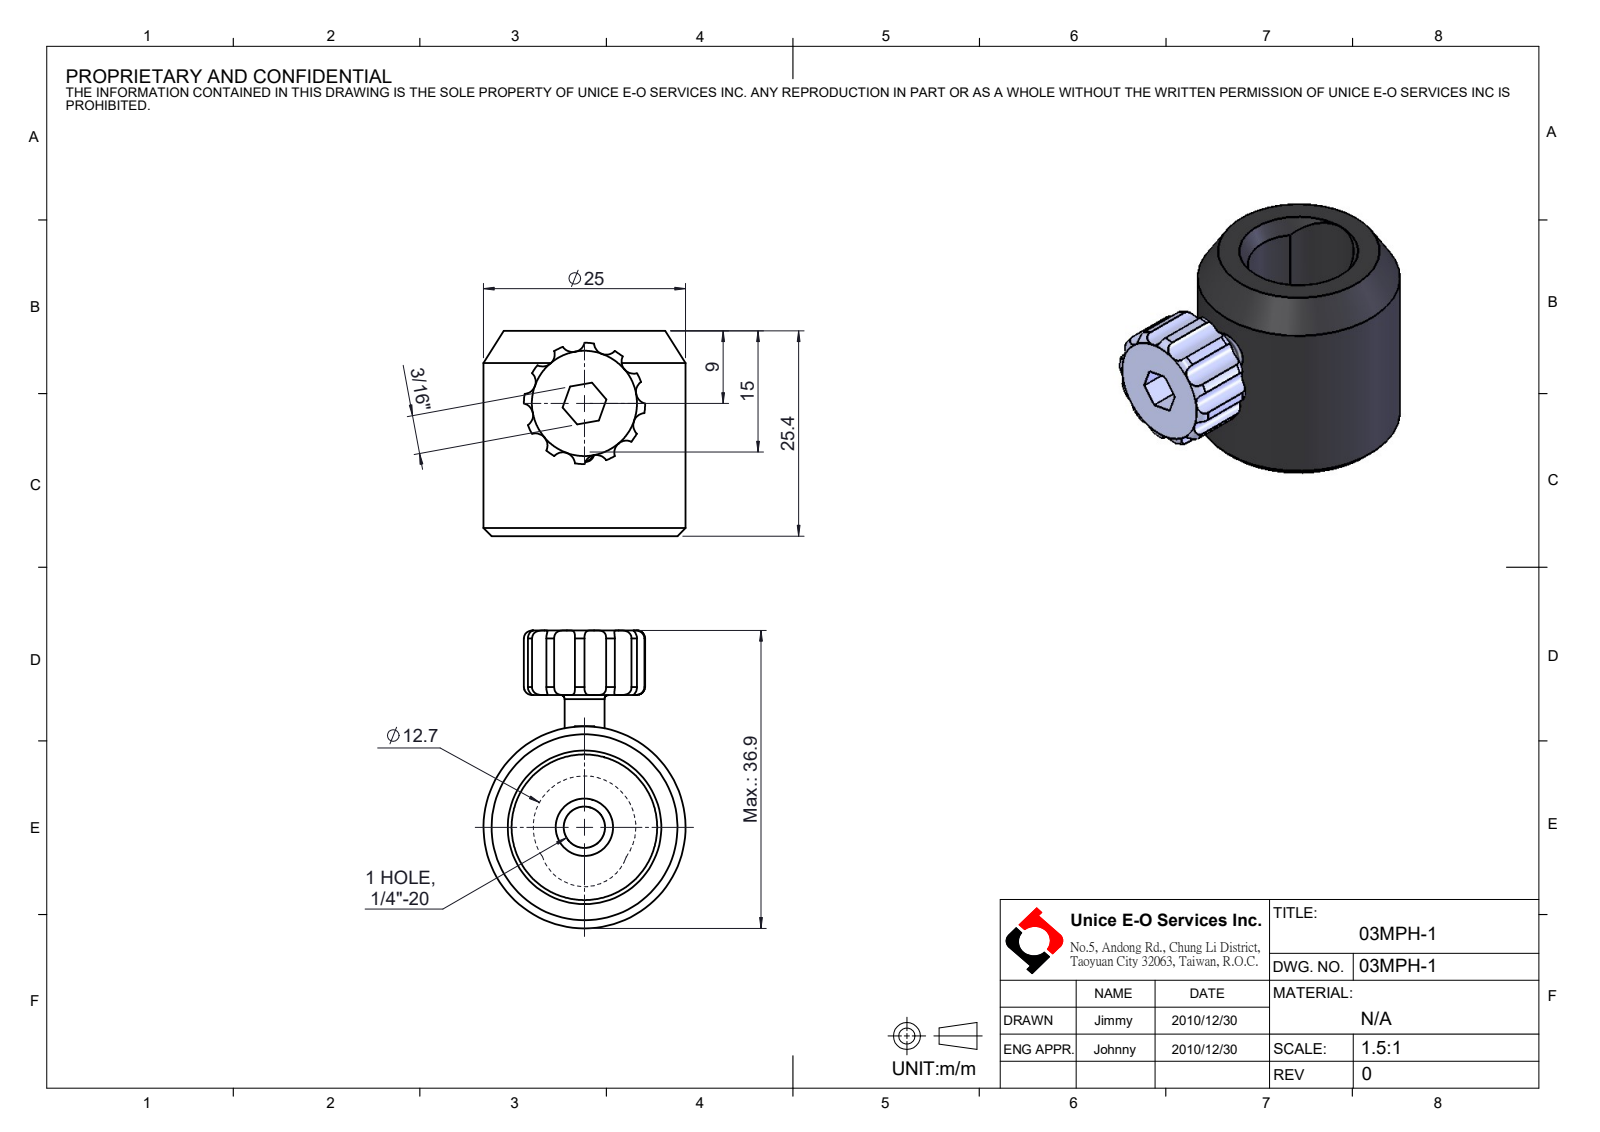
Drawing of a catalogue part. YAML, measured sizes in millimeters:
part_name: "03MPH-1"
step_written_by: "SolidWorks 2016 (CONFIG_CONTROL_DESIGN)"
units: millimeters
bodies: {solids: 0, faces: 100, planar: 16, cylindrical: 44, other: 40}
overall_size: [36.85, 25.4, 25]
round_holes:
  - {diameter: 2.5, count: 1}
  - {diameter: 5, count: 1}
  - {diameter: 5.11, count: 1}
  - {diameter: 19, count: 1}
round_bosses_or_shafts:
  - {diameter: 25, count: 1}
  - {diameter: 4.94, count: 1}
partial_cylinders:
  - {radius: 1.5, count: 12}
  - {radius: 5.5, count: 1}
  - {radius: 6.35, count: 1}
  - {radius: 7.5, count: 1}
face_to_face_distances: [25.4, 8, 4.76, 4.77, 3.85, 11.85, 1.5]
hole_center_spacings: [6]
